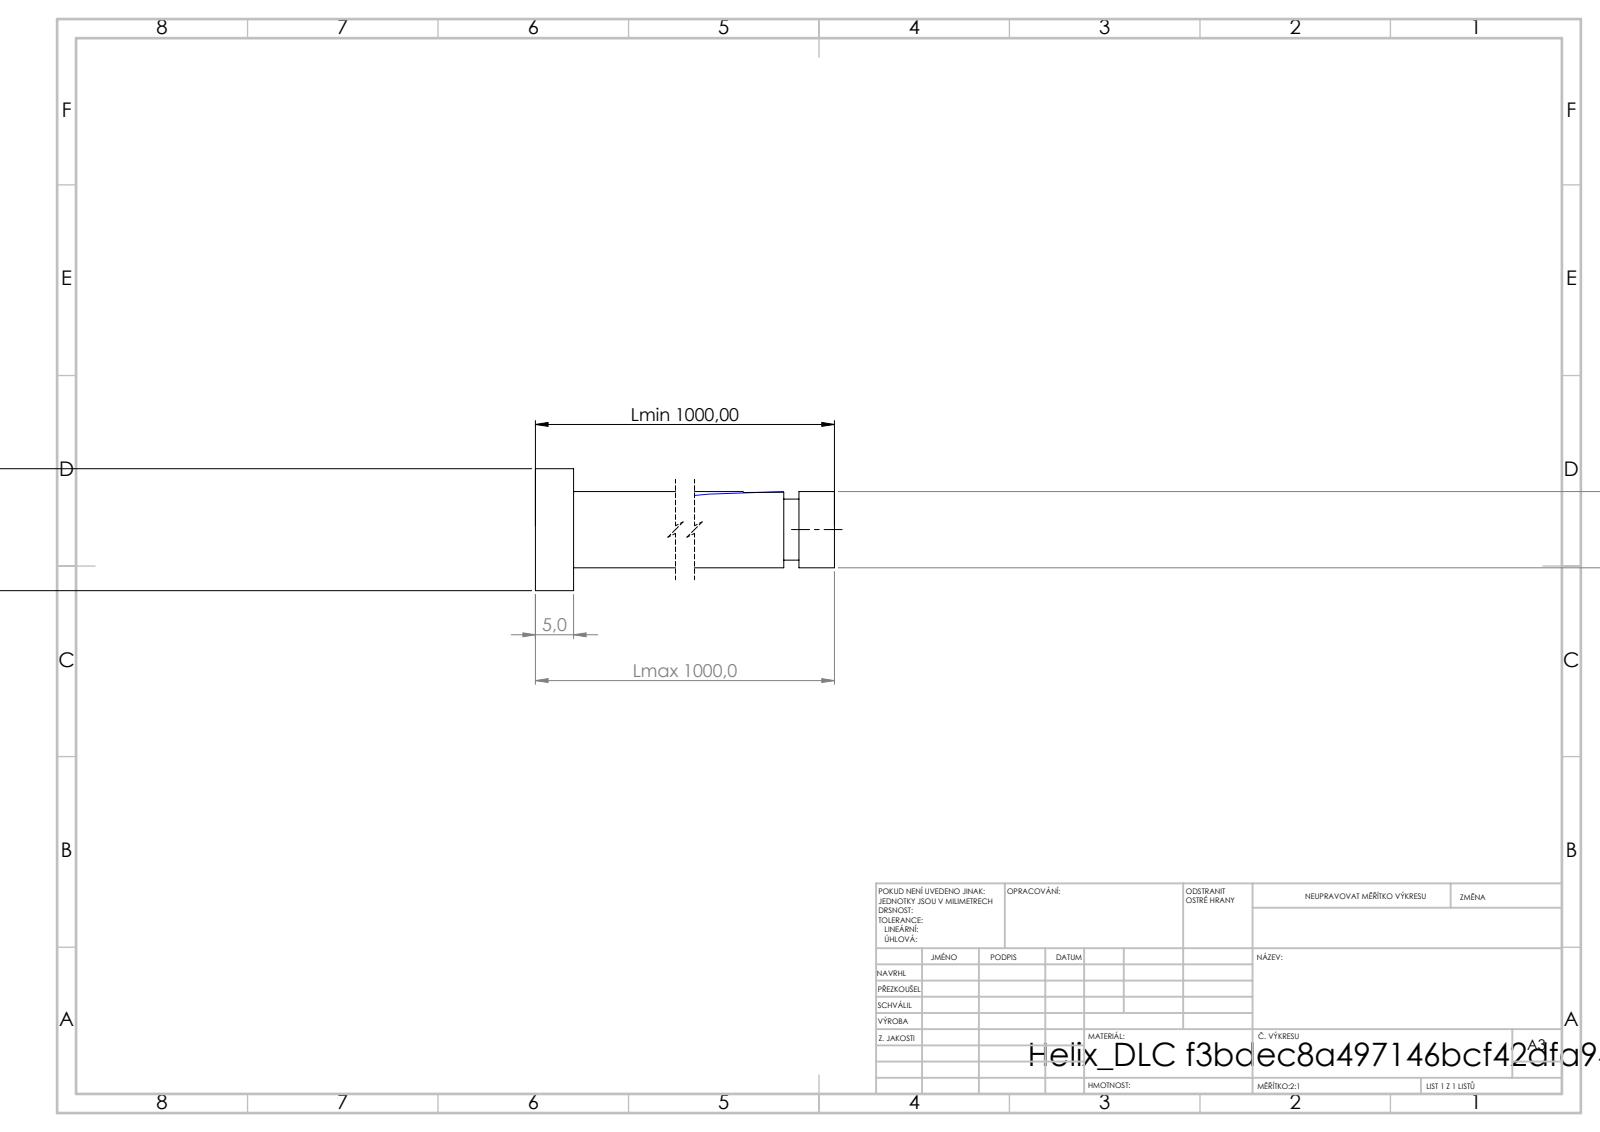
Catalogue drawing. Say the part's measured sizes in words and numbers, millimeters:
Its 3-D file was written by "SolidWorks 2019 (CONFIG_CONTROL_DESIGN)". It is 1 solid with 16 faces: 6 planar, 9 cylindrical and 1 other. Overall it measures 1000 by 16 by 16 millimeters. Its volume is 95 798 cubic millimeters and its surface area 42 910 square millimeters. Round bosses or shafts: 1 of diameter 16, 1 of diameter 10, 1 of diameter 8. The main face-to-face distances are 5, 1000, 995, 995.35, 990.35, 4.65, 993.35, 988.35, 2, 6.65.
